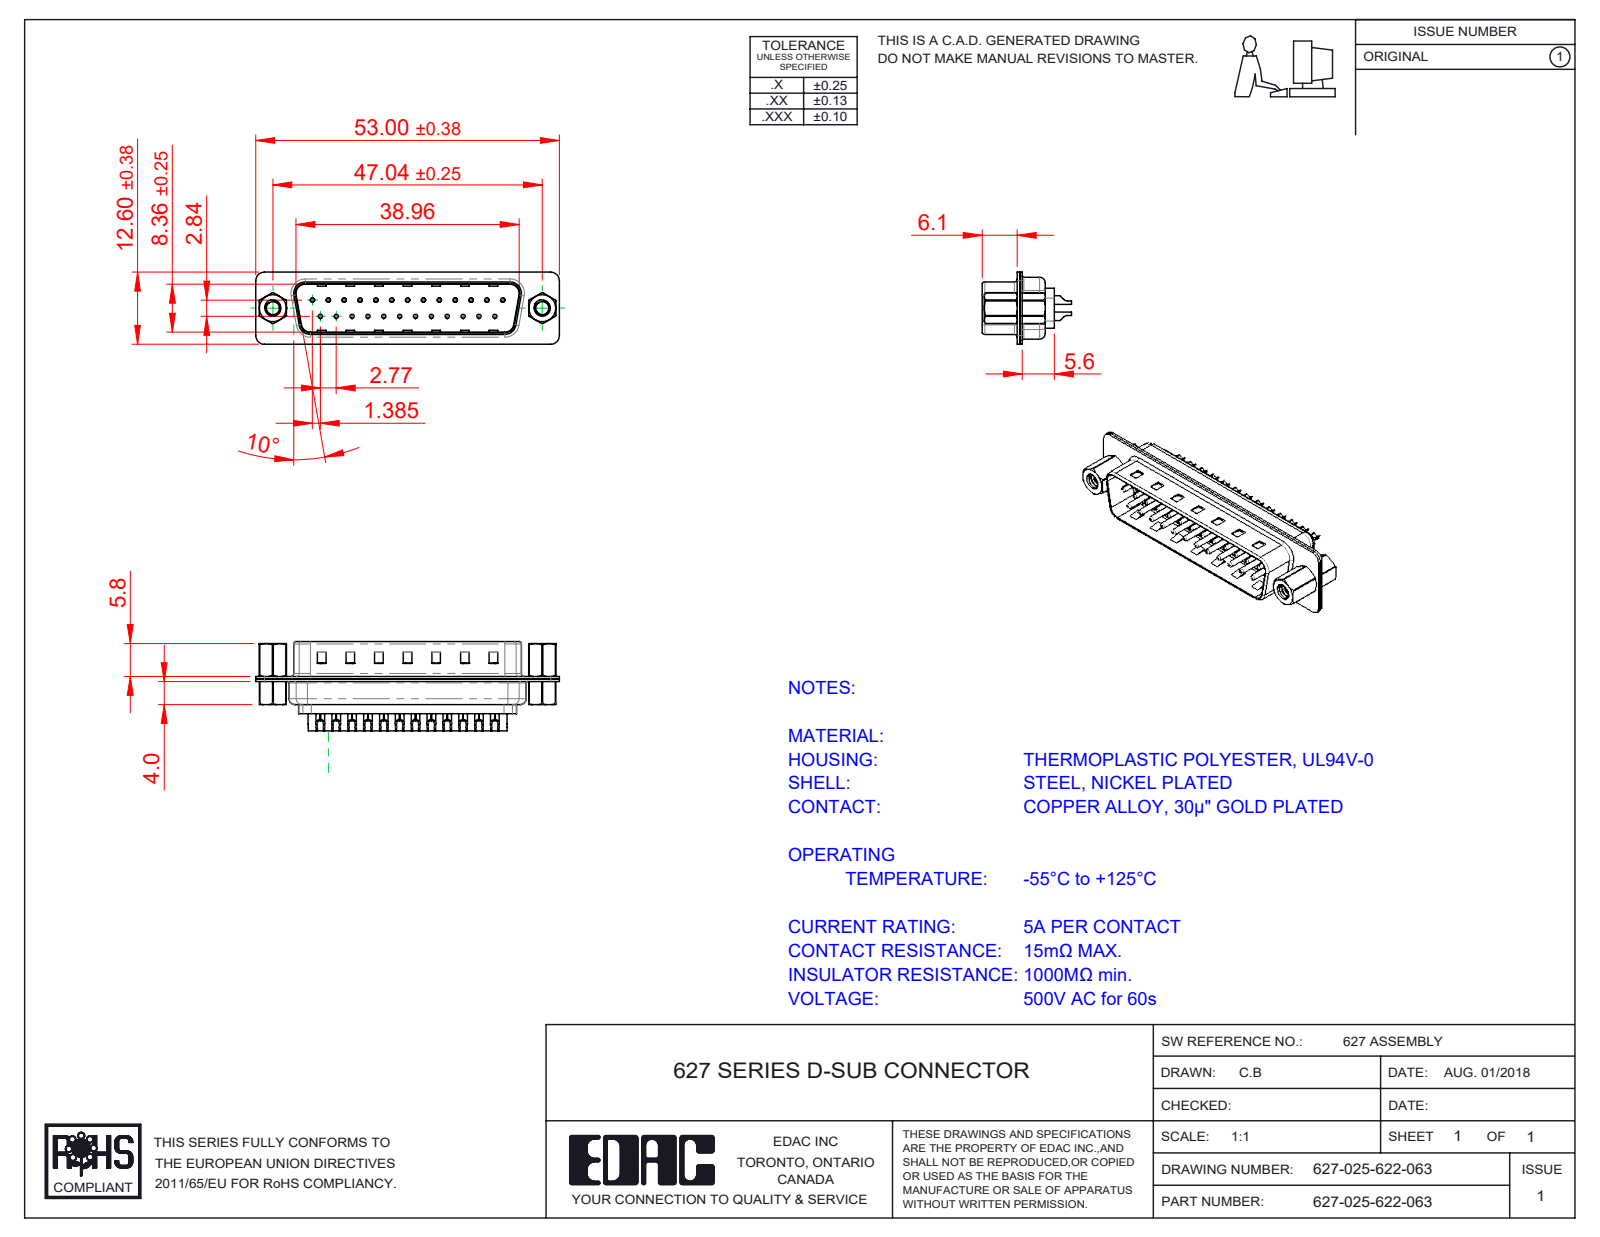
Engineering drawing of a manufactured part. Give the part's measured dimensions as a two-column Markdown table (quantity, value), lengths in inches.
| quantity | value |
| --- | --- |
| part name | 627 Housing_25 LP; 627 Contact Row 1_22L; 627 Shell Front_25 Contacts; 627 4-40 Threaded Rivet (+4 more) |
| STEP written by | SolidWorks 2020 (CONFIG_CONTROL_DESIGN) |
| units | inches |
| bodies | 32 solids, 2098 faces (543 planar, 932 cylindrical, 623 other) |
| overall size | 2.087 × 0.604 × 0.496 |
| volume | 0.177 in³ |
| surface area | 12.91 in² |
| round holes (diameter × count) | 0.014 × 25, 0.043 × 25, 0.063 × 25, 0.089 × 2, 0.09 × 2, 0.157 × 2, 0.189 × 2 |
| round bosses / shafts (diameter × count) | 0.079 × 25, 0.059 × 25, 0.03 × 25, 0.197 × 2, 0.193 × 2, 0.11 × 2 |
| partial cylindrical surfaces (radius × count) | 0.059 × 16, 0.079 × 12, 0.02 × 8, 0.063 × 8, 0.039 × 6, 0.01 × 4, 0.024 × 4, 0.026 × 4 |
| main face-to-face distances | 0.016, 0.018, 0.032, 0.377, 0.345, 0.035, 0.059, 0.055, 0.256, 0.238 |
| hole center spacings | 0.124, 0.327, 0.109, 0.218, 0.436, 0.654, 0.198, 0.198 |
